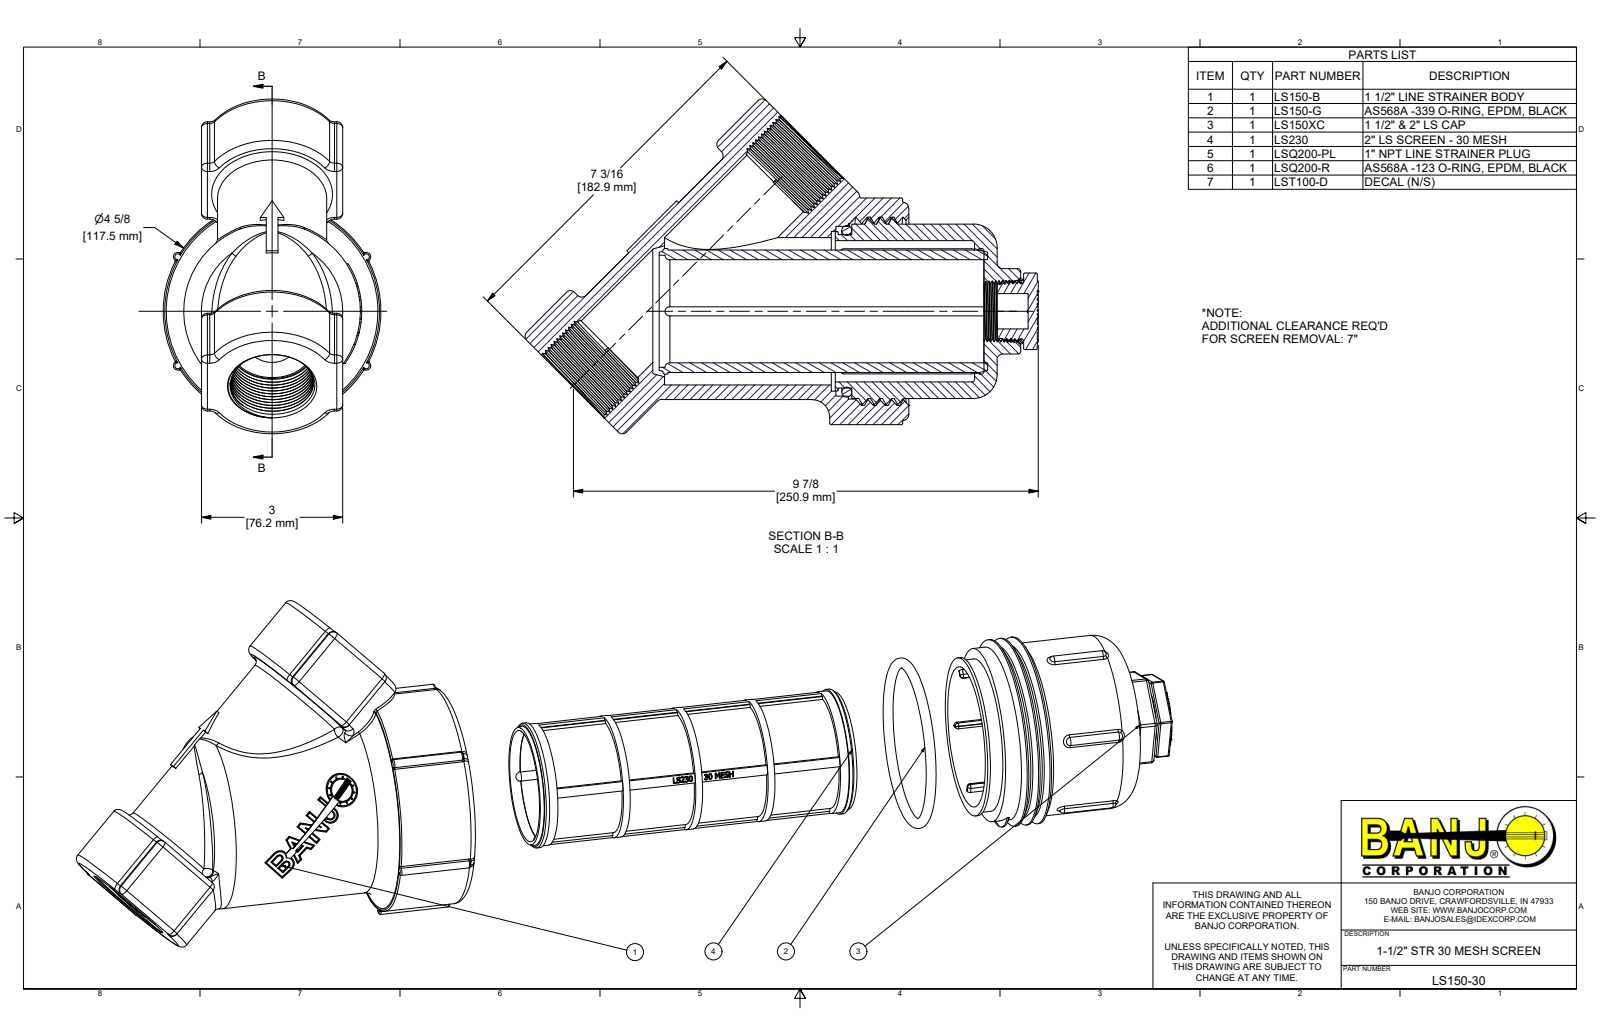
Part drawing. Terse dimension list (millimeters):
name: LS150-B; LS150XC; LSQ200-PL; LSQ200-R (+4 more)
written by: Autodesk Inventor 2014 (AUTOMOTIVE_DESIGN)
unit: mm
bodies: 5 solids, 1438 faces (658 planar, 262 cylindrical, 518 other)
size: 276.98 × 180.39 × 117.47
volume: 963 938 mm³; area: 311 064 mm²
holes: 2× ⌀43.18, 2× ⌀44.73, 1× ⌀11.53, 1× ⌀16.29, 1× ⌀19.05, 1× ⌀29.87, 1× ⌀55.63, 1× ⌀59.69, 1× ⌀76.2, 1× ⌀79.5, 1× ⌀86.23, 1× ⌀91.57
bosses: 1× ⌀117.47, 1× ⌀95.25, 1× ⌀94.04, 1× ⌀85.85, 1× ⌀82.73, 1× ⌀67.72, 1× ⌀66.04, 1× ⌀60.45
rounds: 46× R1.52, 35× R3.17, 30× R0.76, 12× R2.38, 4× R2.54, 3× R3.05, 2× R1.66, 2× R2.09
face distances: 36.7, 76.2, 182.6, 80.26, 40.51, 175.34, 95.08, 44.32, 34.04, 5.08
